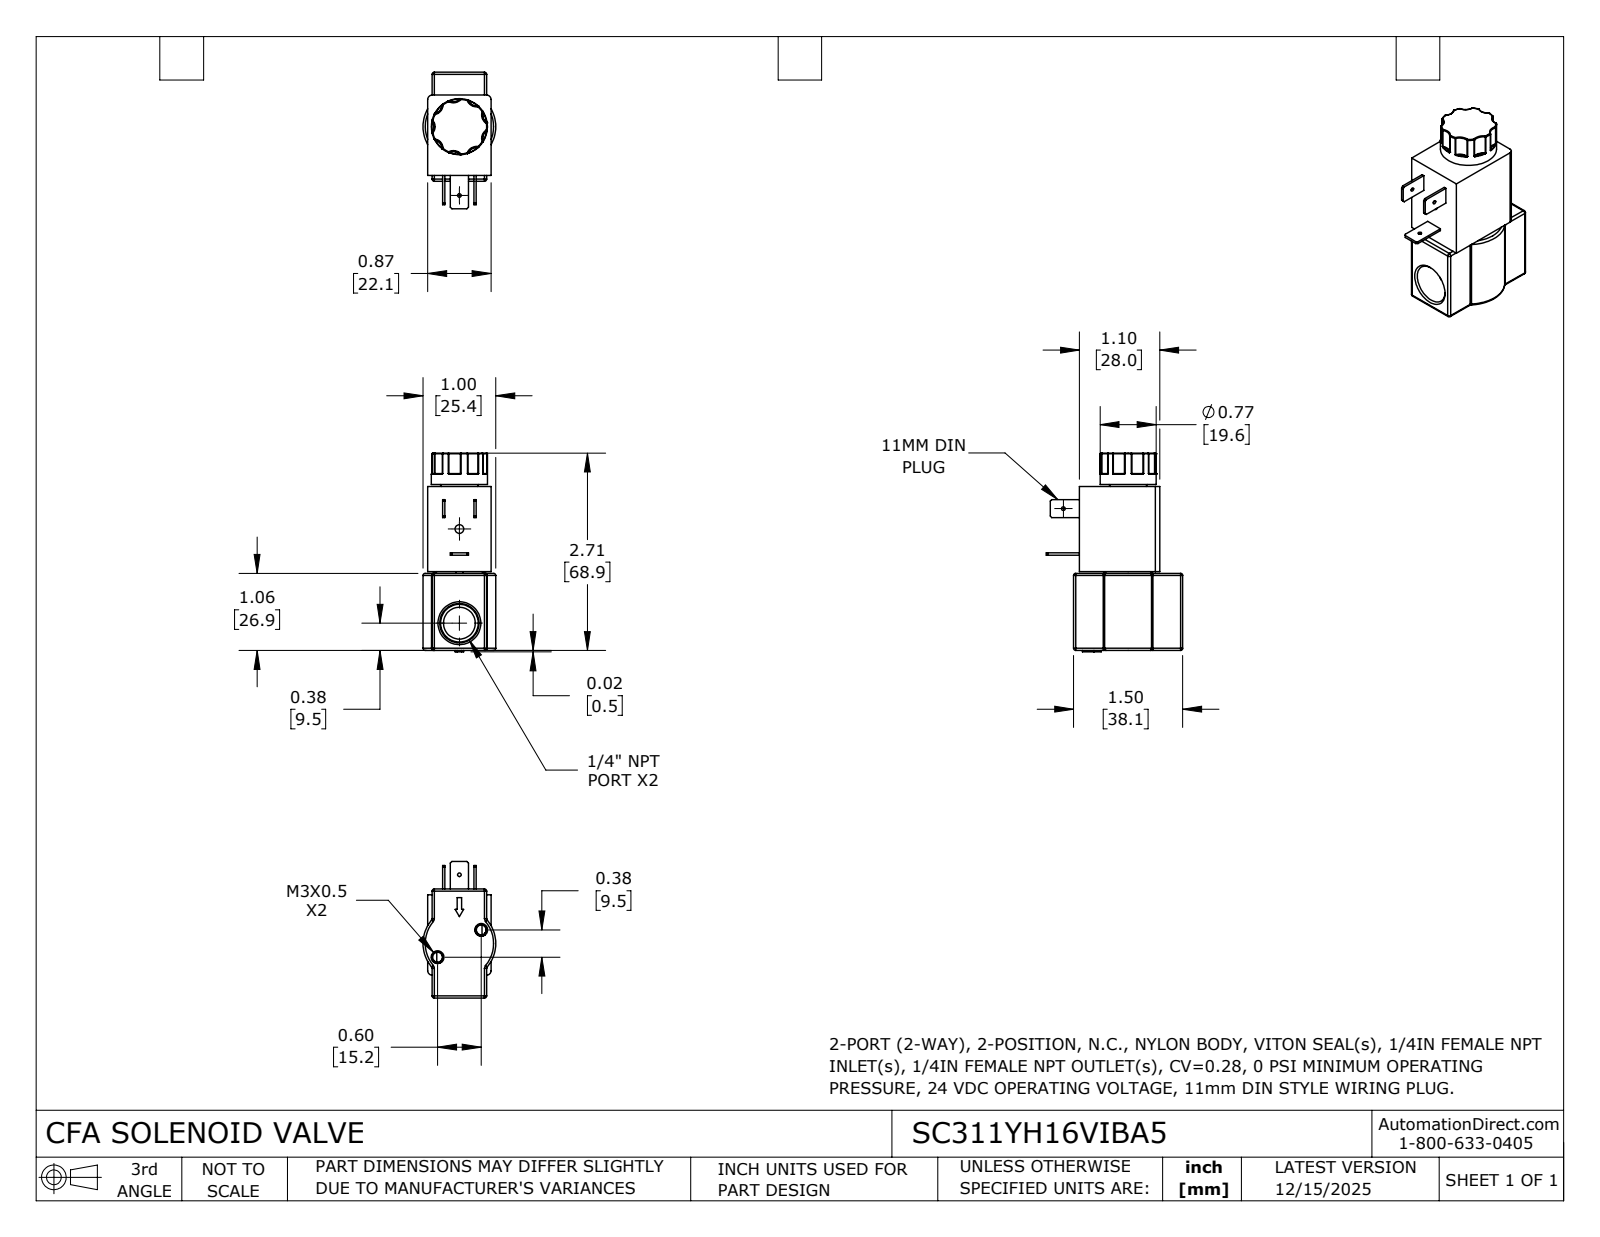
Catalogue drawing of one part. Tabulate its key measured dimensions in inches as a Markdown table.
| quantity | value |
| --- | --- |
| part name | SC311YH16VIBA5 |
| STEP written by | SolidWorks 2024 (CONFIG_CONTROL_DESIGN) |
| units | inches |
| bodies | 1 solid, 383 faces (62 planar, 117 cylindrical, 204 other) |
| overall size | 2.732 × 1.877 × 1 |
| volume | 2.397 in³ |
| surface area | 17.71 in² |
| round holes (diameter × count) | 0.05 × 2, 0.136 × 2, 0.12 × 1, 0.438 × 1 |
| round bosses / shafts (diameter × count) | 0.77 × 1 |
| partial cylindrical surfaces (radius × count) | 0.01 × 18, 0.03 × 16, 0.133 × 7, 0.06 × 2, 0.132 × 2, 0.295 × 2, 0.311 × 1, 0.5 × 1 |
| main face-to-face distances | 0.06, 0.81, 0.87, 1.104, 2.252, 1.06, 1.192, 0.75, 1.085, 0.025 |
| hole center spacings | 0.707, 0.815, 1.172, 1.293 |
